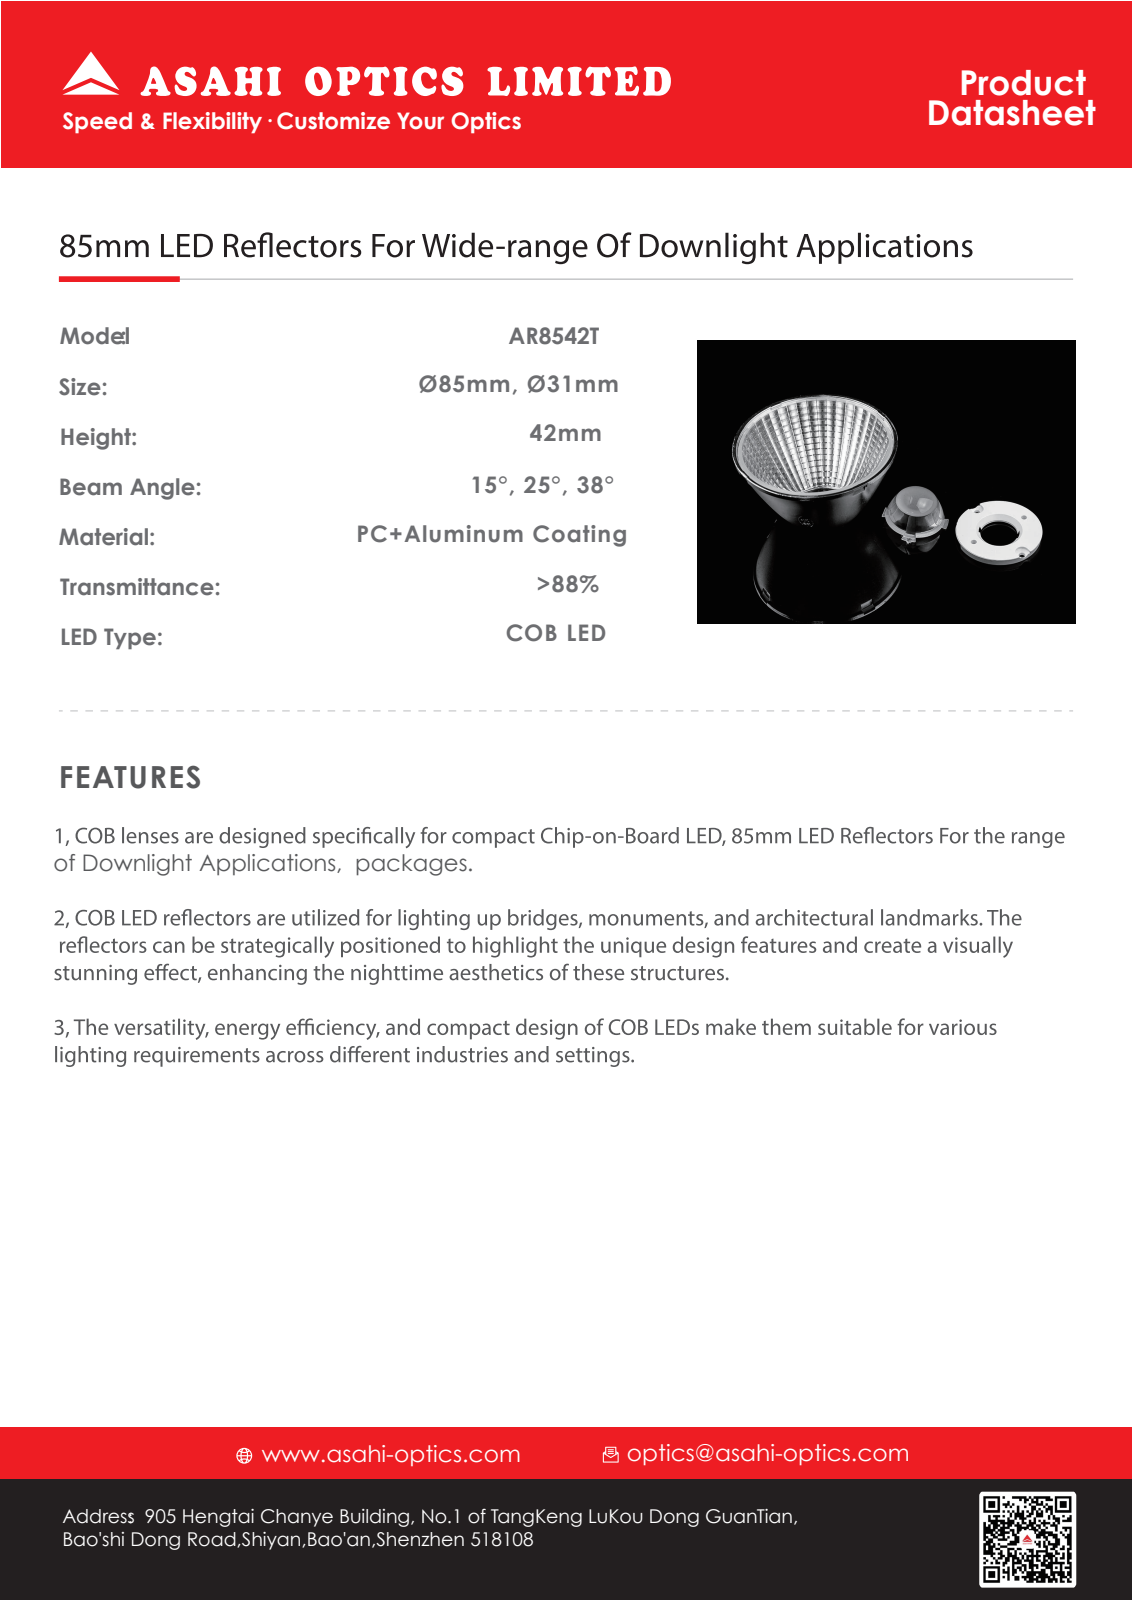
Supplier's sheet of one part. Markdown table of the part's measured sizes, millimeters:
| quantity | value |
| --- | --- |
| part name | 8542T |
| STEP written by | SolidWorks 2016 (AUTOMOTIVE_DESIGN) |
| units | millimeters |
| bodies | 1 solid, 64 faces (28 planar, 14 cylindrical, 22 other) |
| overall size | 85 × 85 × 42 |
| volume | 22 316 mm³ |
| surface area | 20 572 mm² |
| round holes (diameter × count) | 31 × 1, 81.5 × 1 |
| round bosses / shafts (diameter × count) | 85 × 1 |
| partial cylindrical surfaces (radius × count) | 40.25 × 1 |
| main face-to-face distances | 1, 39, 40, 2, 42, 3, 41, 38 |
